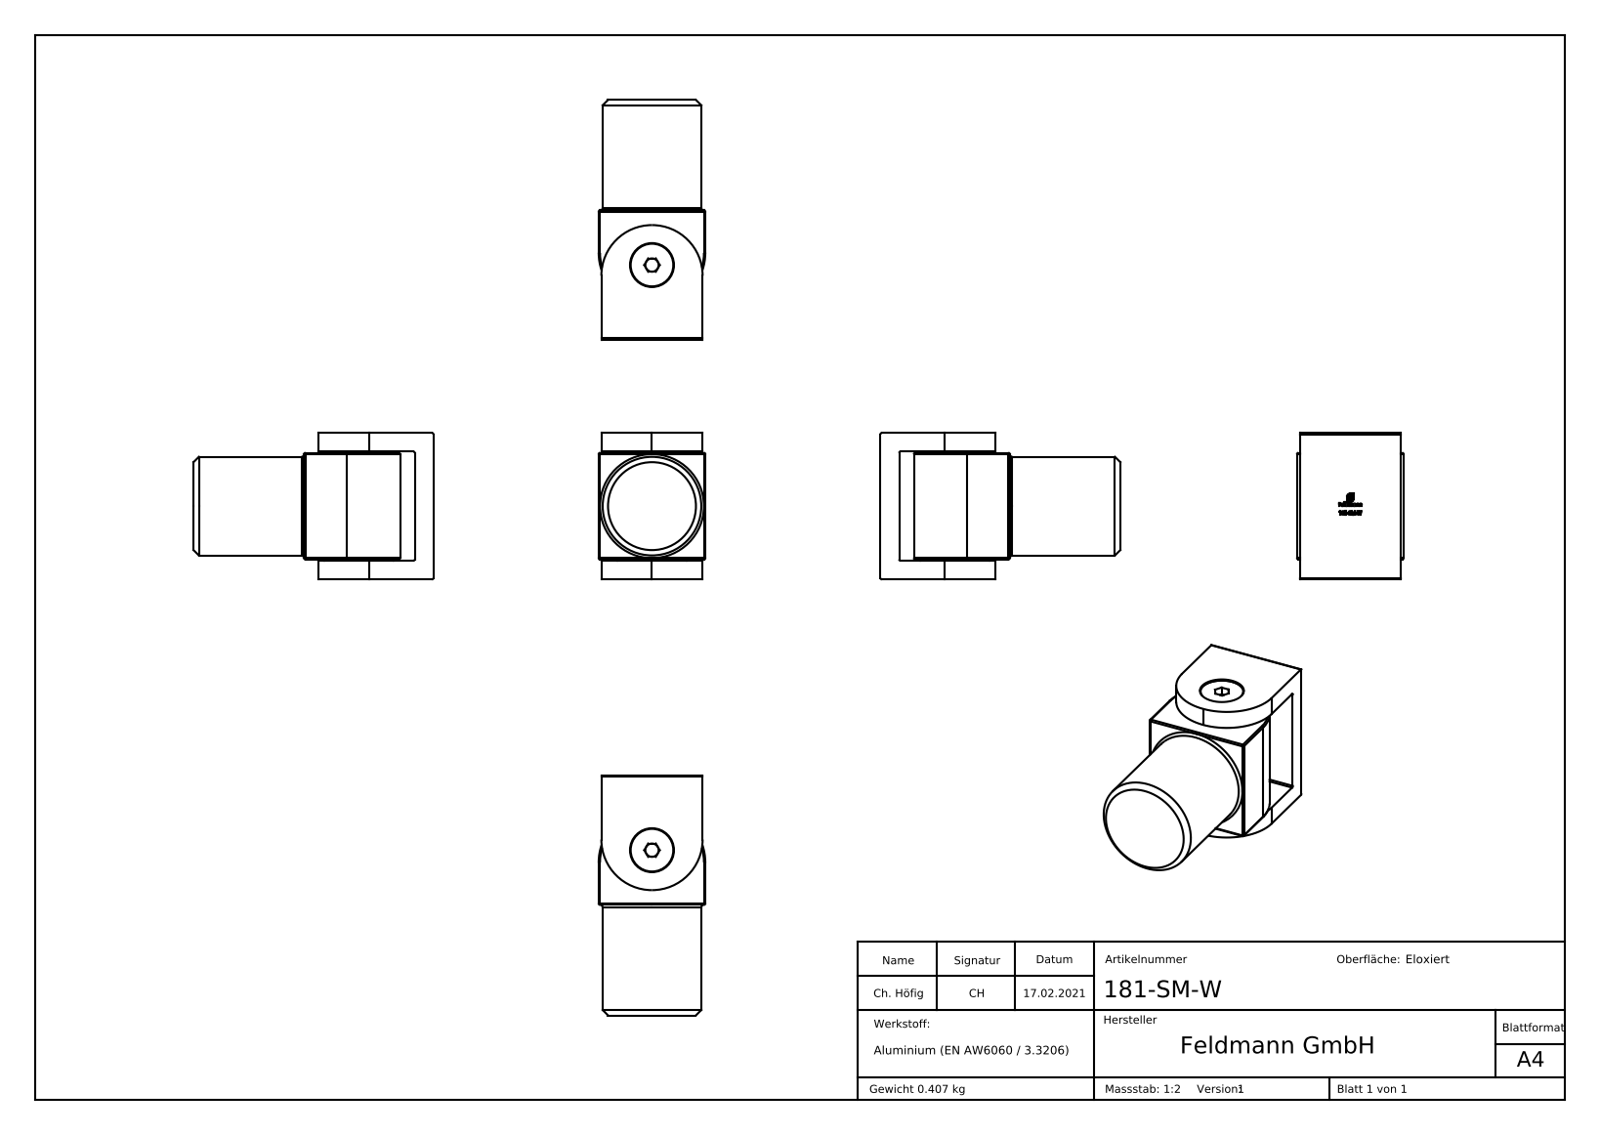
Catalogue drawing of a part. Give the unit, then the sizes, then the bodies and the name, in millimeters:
Units: millimetres
Overall size (bounding box): 14000.35 × 6000 × 6000
Round holes (diameter × count): ⌀6.8 ×1, ⌀8.5 ×1, ⌀16.5 ×1, ⌀19 ×1, ⌀23.6 ×1, ⌀26 ×1
Round bosses / shafts (diameter × count): ⌀37 ×1, ⌀23.4 ×1, ⌀18.8 ×1, ⌀16 ×1, ⌀8 ×1
Partial cylindrical surfaces — rounded edges, fillets, slot ends (radius × count): R0.5 ×12, R19 ×1, R20 ×1
Main face-to-face distances: 7, 48, 41.5, 0.5, 41, 7.5, 47.5, 40.5, 1, 40
Volume: 126 228 mm³ · Surface area: 36 703 mm²
Bodies: 11 solids, 491 faces (209 planar, 76 cylindrical, 206 other)
Part name (STEP PRODUCT): Teil1; Teil2_181-SM-W Teil2; 181-SM-W; Teil3 (+7 more)
STEP written by: SolidWorks 2018 (CONFIG_CONTROL_DESIGN)
